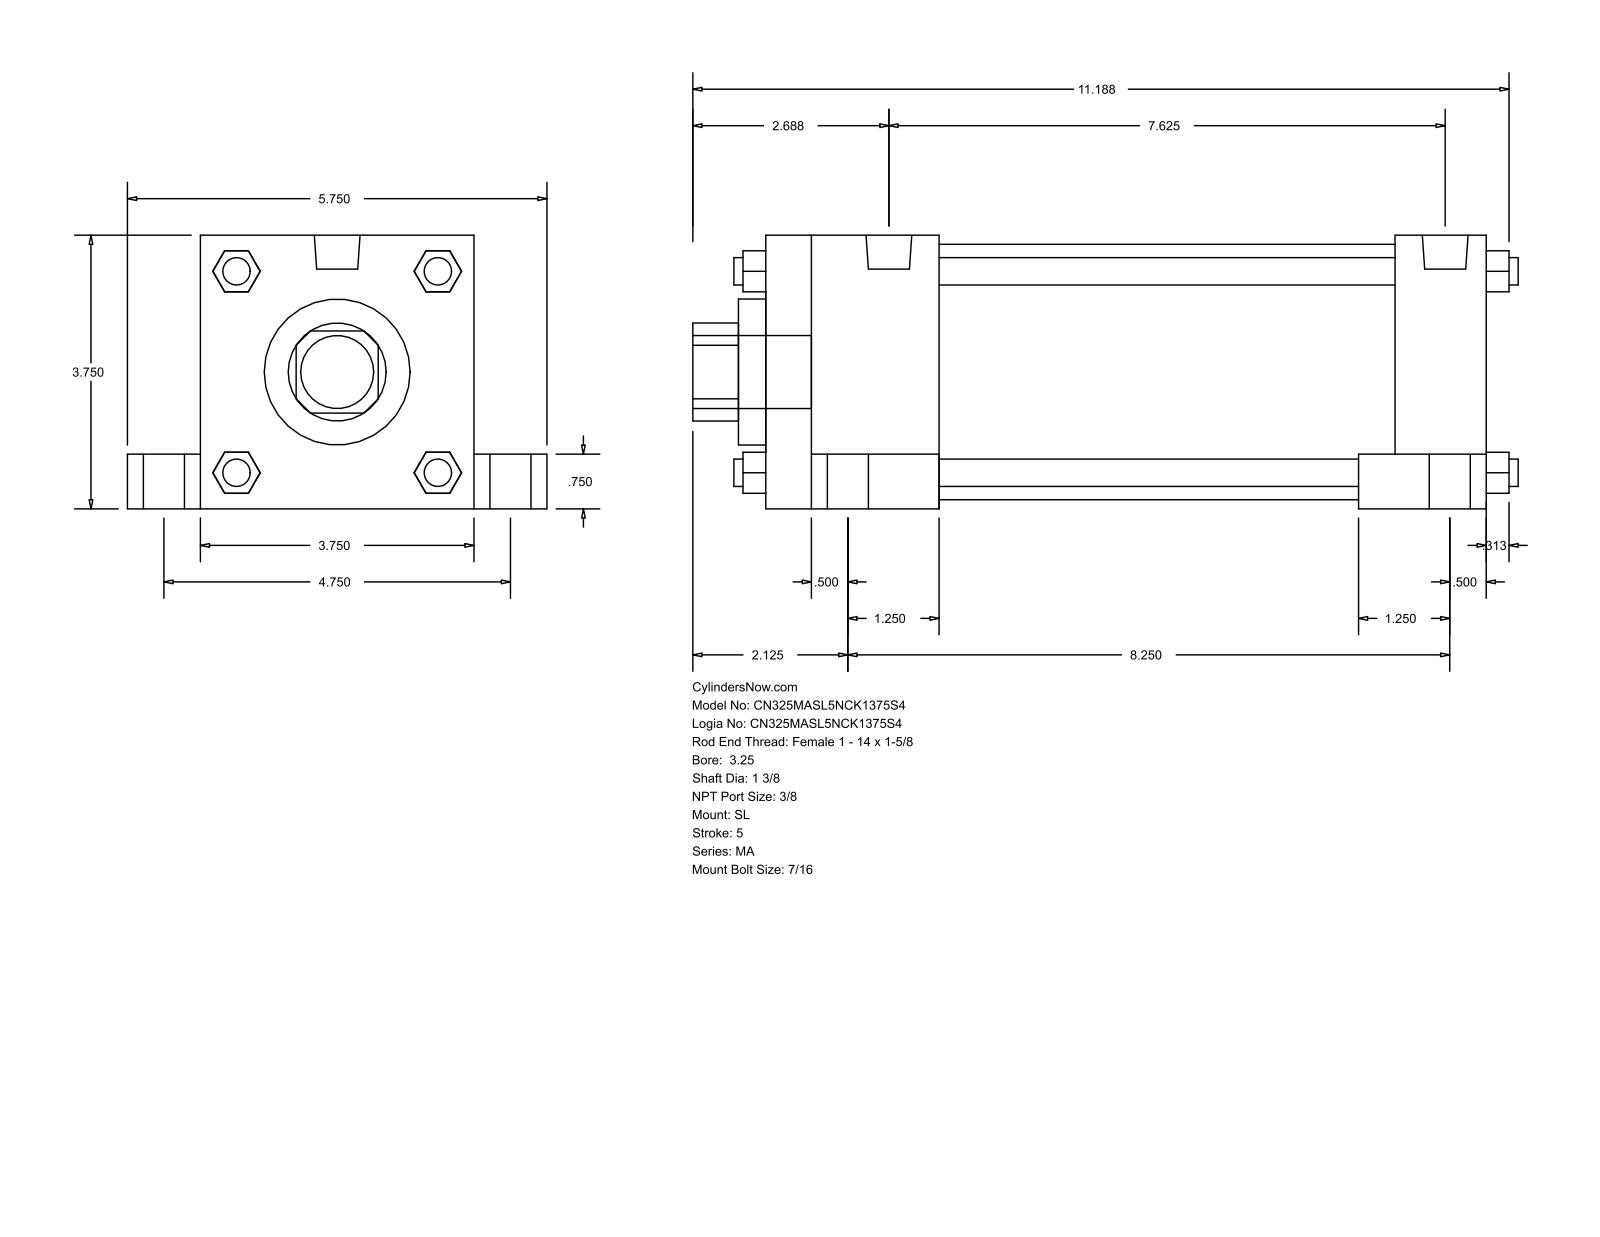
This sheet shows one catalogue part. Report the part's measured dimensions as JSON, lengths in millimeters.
{"part_name": "MA_SL__0325_1.375", "step_written_by": "GSSL Pune (CONFIG_CONTROL_DESIGN)", "units": "millimeters", "bodies": {"solids": 0, "faces": 148, "planar": 112, "cylindrical": 36, "other": 0}, "overall_size": [287.34, 146.05, 95.25], "round_holes": [[34.92, 1], [50.8, 1], [88.9, 1]], "round_bosses_or_shafts": [[20.64, 4], [14.29, 4], [11.11, 4], [9.53, 4], [15.93, 2], [25.4, 1]], "partial_cylinders_radius": [[17.06, 1]], "face_to_face_distances": [95.24, 250.83, 158.75, 25.41, 120.65, 219.07, 31.76, 60.32, 190.51, 19.05]}
